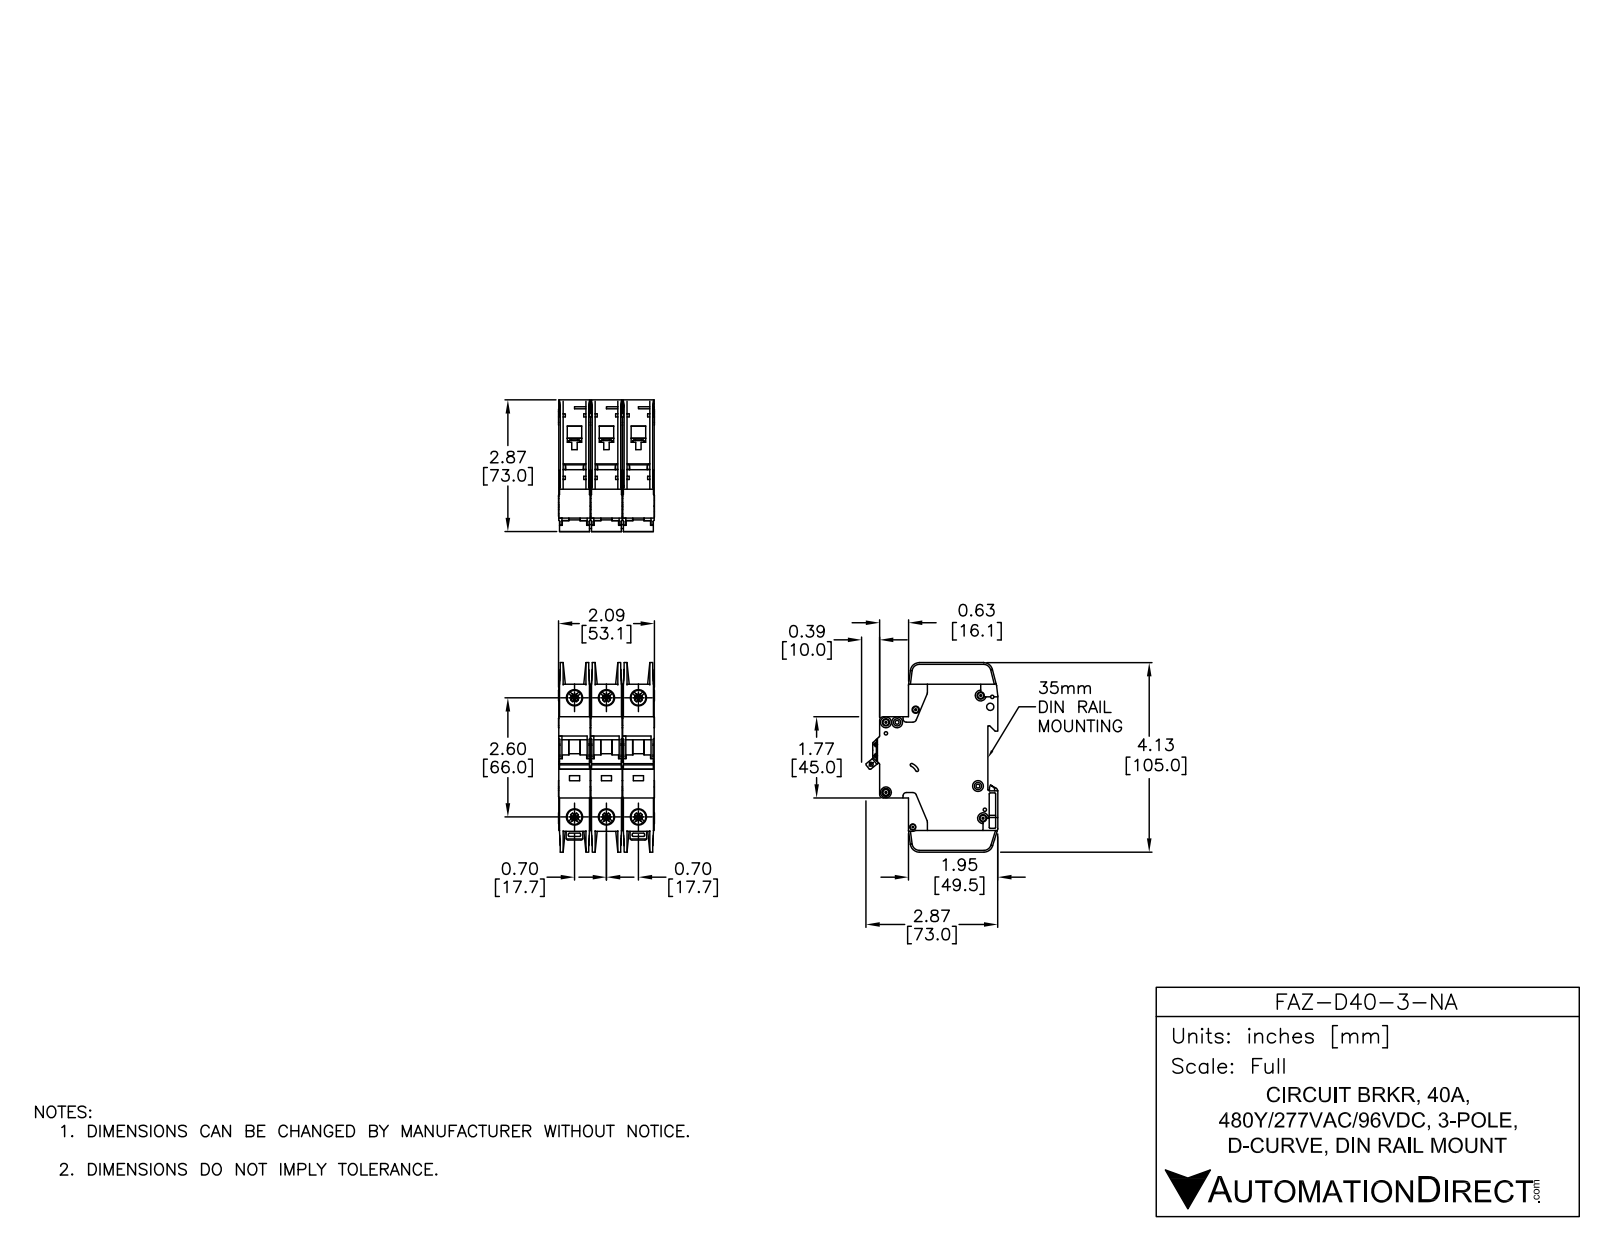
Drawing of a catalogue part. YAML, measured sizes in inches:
part_name: "FAZ-D40-3-NA"
step_written_by: "SolidWorks 2014 (AUTOMOTIVE_DESIGN)"
units: inches
bodies: {solids: 9, faces: 2352, planar: 1227, cylindrical: 789, other: 336}
overall_size: [4.134, 2.876, 2.091]
volume: 14.22
surface_area: 115
round_holes:
  - {diameter: 0.142, count: 7}
  - {diameter: 0.281, count: 6}
  - {diameter: 0.323, count: 6}
  - {diameter: 0.043, count: 2}
  - {diameter: 0.059, count: 2}
  - {diameter: 0.157, count: 2}
  - {diameter: 0.075, count: 1}
  - {diameter: 0.085, count: 1}
  - {diameter: 0.087, count: 1}
  - {diameter: 0.1, count: 1}
  - {diameter: 0.13, count: 1}
  - {diameter: 0.134, count: 1}
round_bosses_or_shafts:
  - {diameter: 0.236, count: 7}
  - {diameter: 0.098, count: 3}
partial_cylinders:
  - {radius: 0.01, count: 65}
  - {radius: 0.02, count: 30}
  - {radius: 0.039, count: 26}
  - {radius: 0.079, count: 14}
  - {radius: 0.071, count: 5}
  - {radius: 0.197, count: 5}
  - {radius: 0.157, count: 4}
  - {radius: 0.008, count: 2}
face_to_face_distances: [0.697, 1.394, 0.689, 1.386, 0.028, 0.593, 0.096, 0.069, 0.62, 0.524]
hole_center_spacings: [0.697, 2.69, 2.598, 0.244, 1.394, 2.948, 0.204, 0.24]
